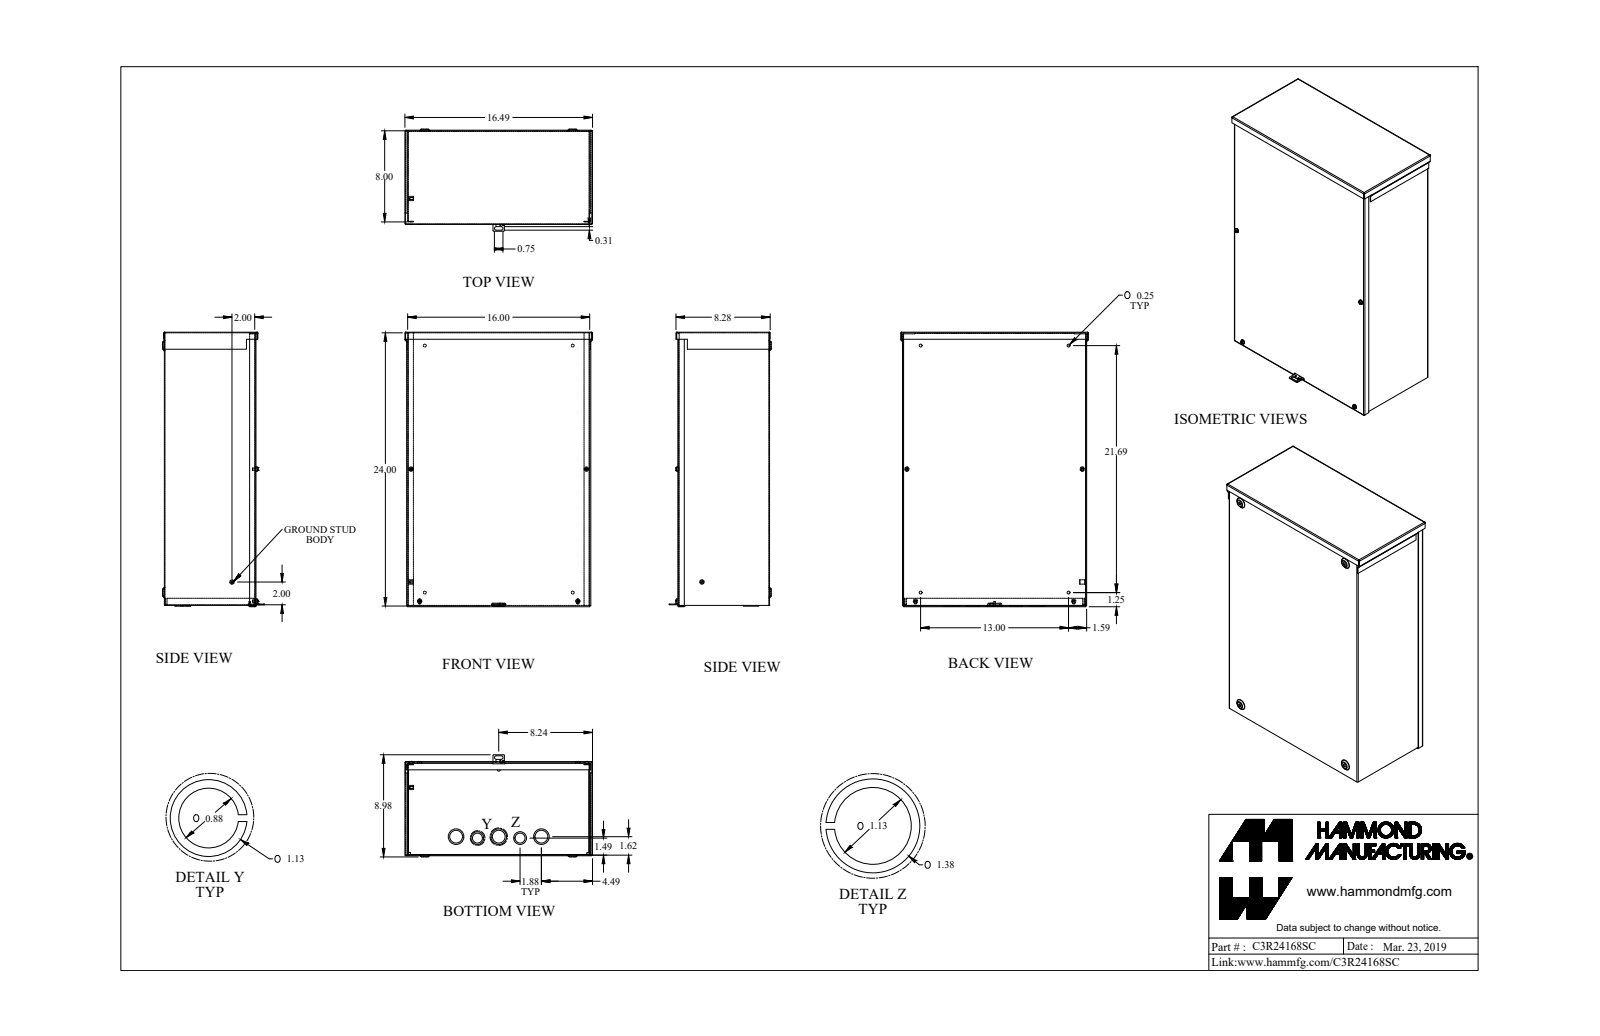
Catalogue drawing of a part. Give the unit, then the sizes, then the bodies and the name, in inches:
Units: inches
Overall size (bounding box): 24.12 × 16.489 × 8.977
Round holes (diameter × count): ⌀0.17 ×4, ⌀0.25 ×4, ⌀1.125 ×3, ⌀0.875 ×2, ⌀0.125 ×1, ⌀0.137 ×1, ⌀0.156 ×1
Round bosses / shafts (diameter × count): ⌀0.19 ×4, ⌀0.375 ×3, ⌀1.375 ×2, ⌀1.125 ×2, ⌀0.375 ×2, ⌀1.375 ×1, ⌀0.125 ×1
Partial cylindrical surfaces — rounded edges, fillets, slot ends (radius × count): R0.029 ×21, R0.086 ×21, R0.109 ×8, R0.125 ×8, R0.156 ×2
Main face-to-face distances: 0.057, 8, 7.943, 8.057, 15.943, 16, 15.886, 0.057, 23.886, 23.943
Hole centre spacings: 10.913, 17.874, 3.75, 0.955, 1.879, 1.88, 6.291, 6.974
Volume: 87.79 in³ · Surface area: 3 095 in²
Bodies: 11 solids, 433 faces (226 planar, 121 cylindrical, 86 other)
Part name (STEP PRODUCT): C3R24168SC_Default
STEP written by: SolidWorks 2019 (CONFIG_CONTROL_DESIGN)
